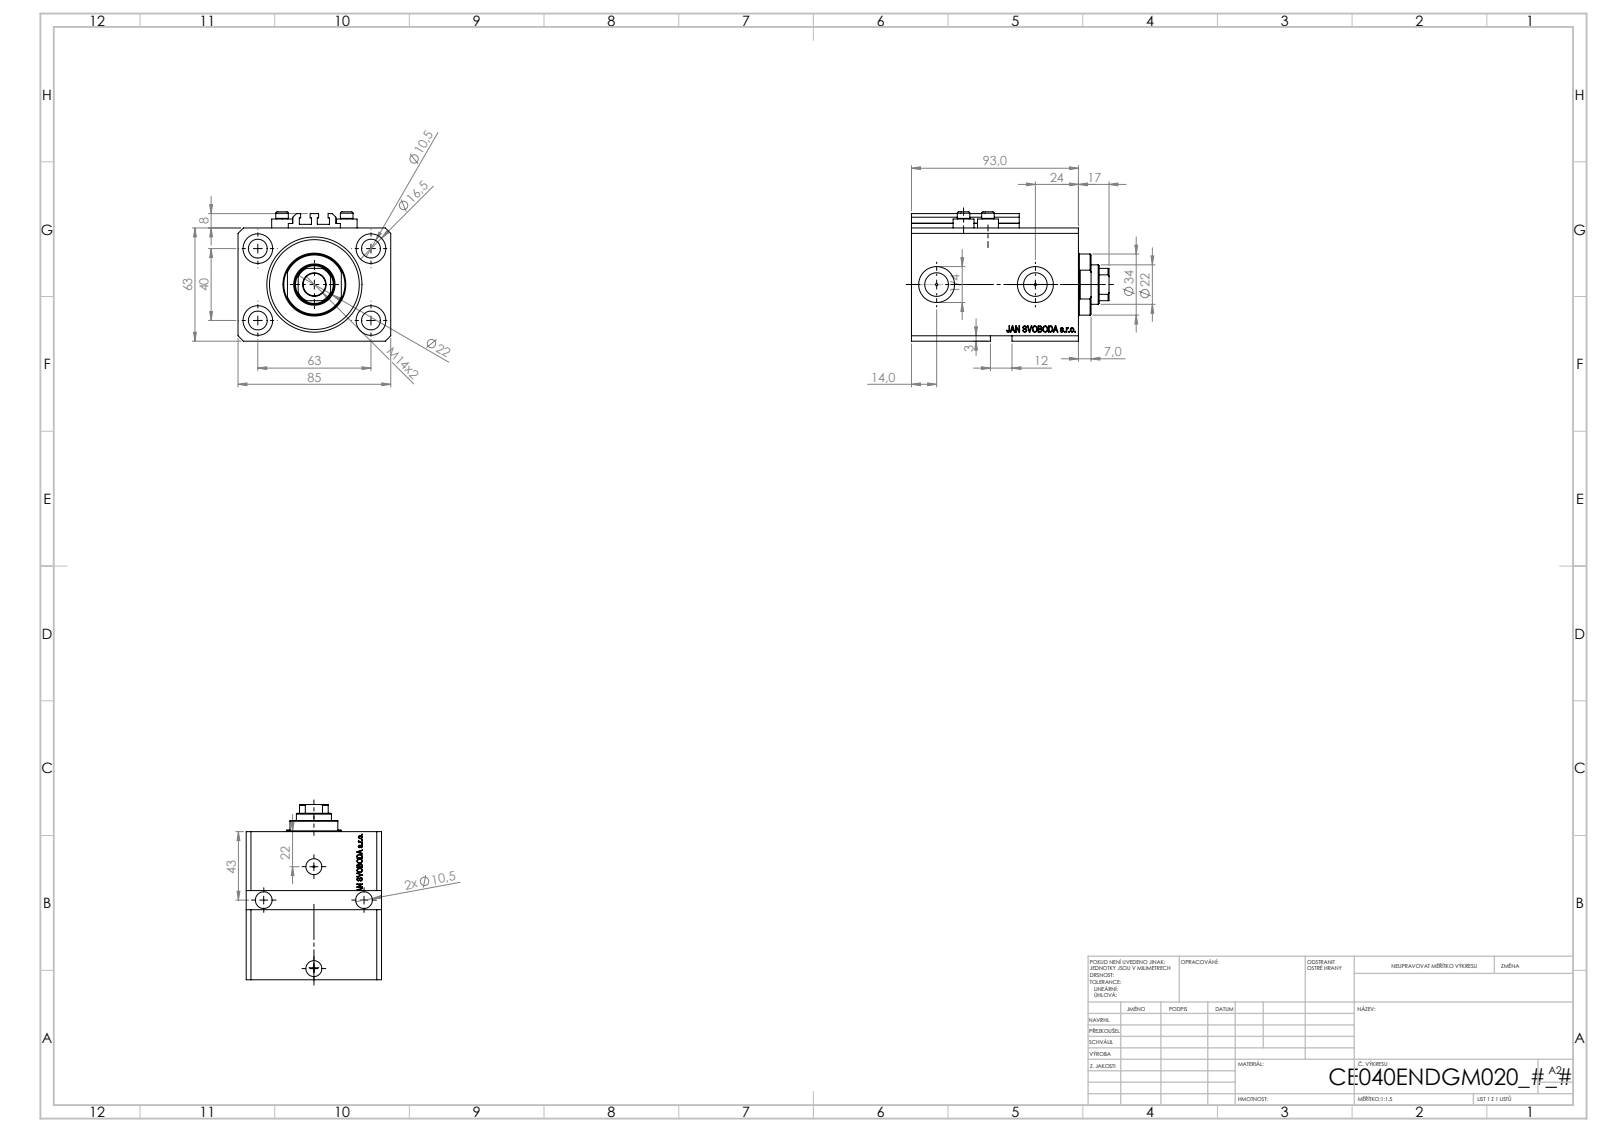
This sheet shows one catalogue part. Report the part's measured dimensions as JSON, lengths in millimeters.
{"part_name": "V250CE_VC_E; ALLEN BOLT V250CE; V250CE_E_Body; V250CE_C_VCP", "step_written_by": "SolidWorks 2019 (CONFIG_CONTROL_DESIGN)", "units": "millimeters", "bodies": {"solids": 8, "faces": 1103, "planar": 539, "cylindrical": 138, "other": 426}, "overall_size": [110, 85, 72], "volume_mm3": 433630, "surface_area_mm2": 96943, "round_holes": [[10.5, 6], [1.25, 4], [4, 4], [16.5, 4], [10, 2], [13.16, 2], [20, 2], [12.5, 1], [22, 1], [40, 1], [53, 1]], "round_bosses_or_shafts": [[11.6, 4], [7, 4], [34, 1]], "partial_cylinders_radius": [[0.2, 10], [10.5, 1]], "face_to_face_distances": [63, 85, 93, 17, 76, 11.4, 64.6, 81.6, 3, 65], "hole_center_spacings": [37.31, 63, 13.6, 15.4, 24.96, 28.02, 28.43, 33.62]}
